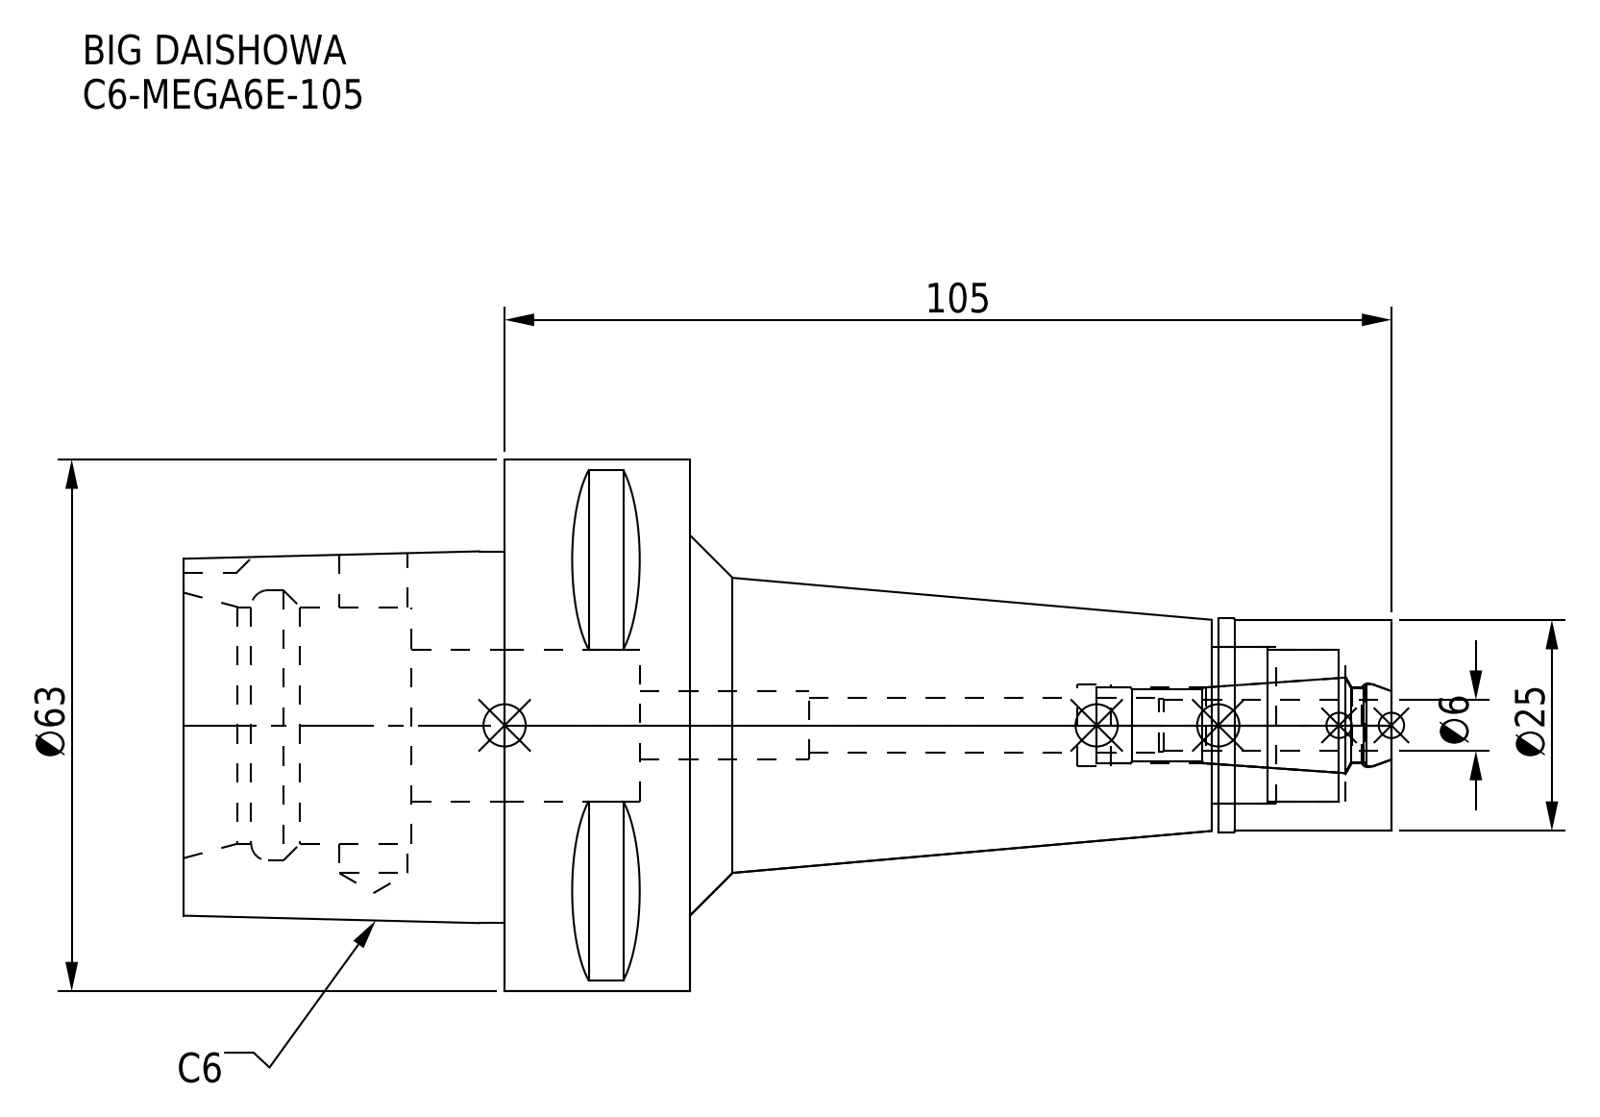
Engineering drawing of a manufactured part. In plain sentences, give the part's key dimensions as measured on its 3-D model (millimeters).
The part is named "C6-MEGA6E-105_1.stp; DXF_TEMP_ASSY_ASM_4_ASM.stp; C6-MEGA6E-105-060.stp; C6-MEGA6E-105-060-FreeParts (+3 more)". Its 3-D file was written by "SolidWorks 2019 (CONFIG_CONTROL_DESIGN)". It is 2 solids with 100 faces: 37 planar, 39 cylindrical and 24 other. Overall it measures 143 by 63 by 63 millimeters. Its volume is 148 645 cubic millimeters and its surface area 31 662 square millimeters. Round holes: 1 of diameter 6.4, 1 of diameter 8, 1 of diameter 8.1, 1 of diameter 9, 1 of diameter 9.6, 1 of diameter 9.9, 1 of diameter 18, 1 of diameter 18.5, 1 of diameter 28, 1 of diameter 32. Round bosses or shafts: 1 of diameter 63, 1 of diameter 25.3, 1 of diameter 25. Partial cylindrical surfaces (rounded edges, fillets, slot ends): 1 of radius 5. The main face-to-face distances are 22, 27, 60, 38, 83, 105, 143, 116, 33, 11.
